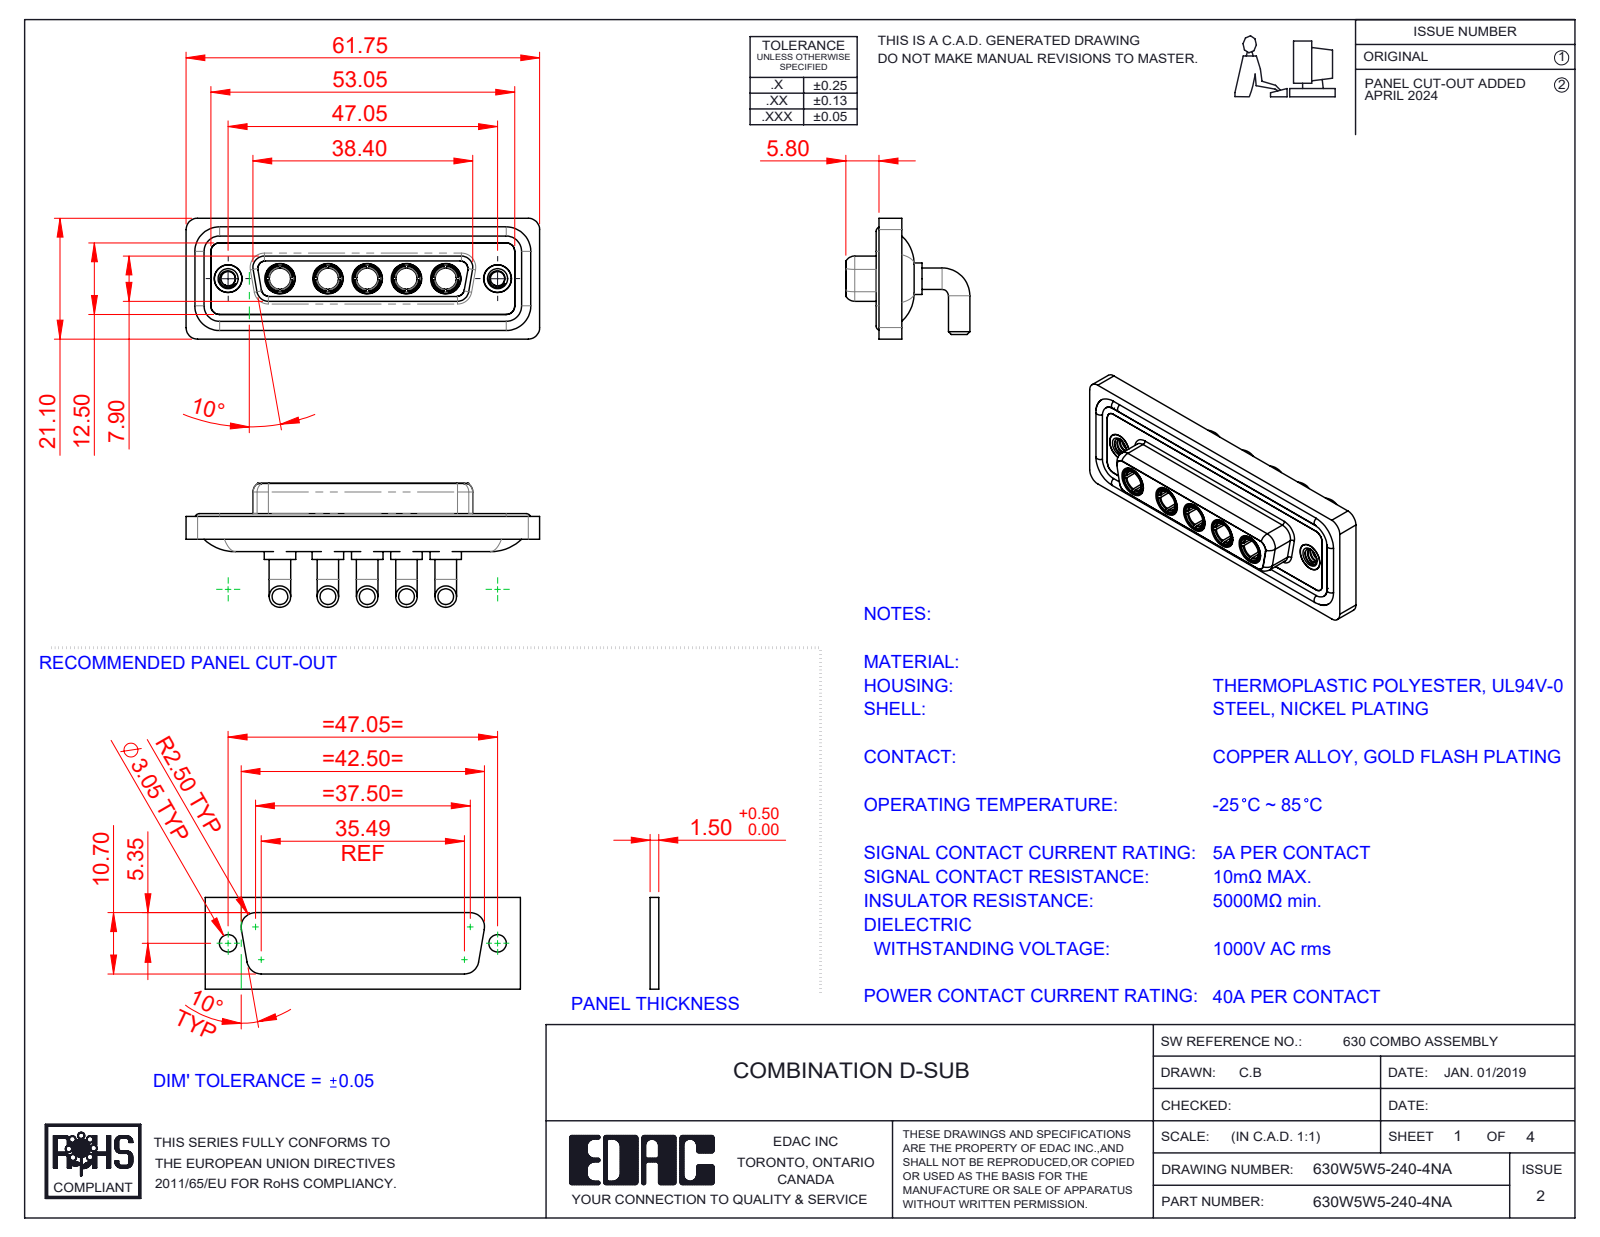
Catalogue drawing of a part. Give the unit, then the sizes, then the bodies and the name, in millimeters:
Units: millimetres
Overall size (bounding box): 61.75 × 21.68 × 21.1
Round holes (diameter × count): ⌀4.85 ×7, ⌀3.7 ×5, ⌀5.3 ×5, ⌀2.5 ×2, ⌀4 ×2, ⌀4.05 ×2, ⌀5 ×2
Round bosses / shafts (diameter × count): ⌀3.75 ×10, ⌀5.5 ×5, ⌀5.2 ×5, ⌀4.96 ×5, ⌀4.75 ×5, ⌀1.6 ×4, ⌀4.95 ×2, ⌀4.8 ×2
Partial cylindrical surfaces — rounded edges, fillets, slot ends (radius × count): R1.5 ×18, R2 ×18, R1.35 ×8, R1.6 ×8, R2.1 ×5, R0.25 ×4, R0.5 ×4, R0.6 ×4
Main face-to-face distances: 0.4, 1.8, 4.1, 1.1, 2.5, 3.1, 3.7, 1.6, 1.5, 2.9
Hole centre spacings: 6.86, 9.04, 38.01, 6.87, 8.38, 13.72, 13.73, 15.25
Volume: 8 791 mm³ · Surface area: 14 035 mm²
Bodies: 17 solids, 770 faces (250 planar, 311 cylindrical, 209 other)
Part name (STEP PRODUCT): 630Combo Waterproof Housing_25 Contacts; 630W5W5-140-4NA; Power Socket_40A RA; 630Combo Shell Front_25 Contacts (+3 more)
STEP written by: SolidWorks 2023 (CONFIG_CONTROL_DESIGN)
